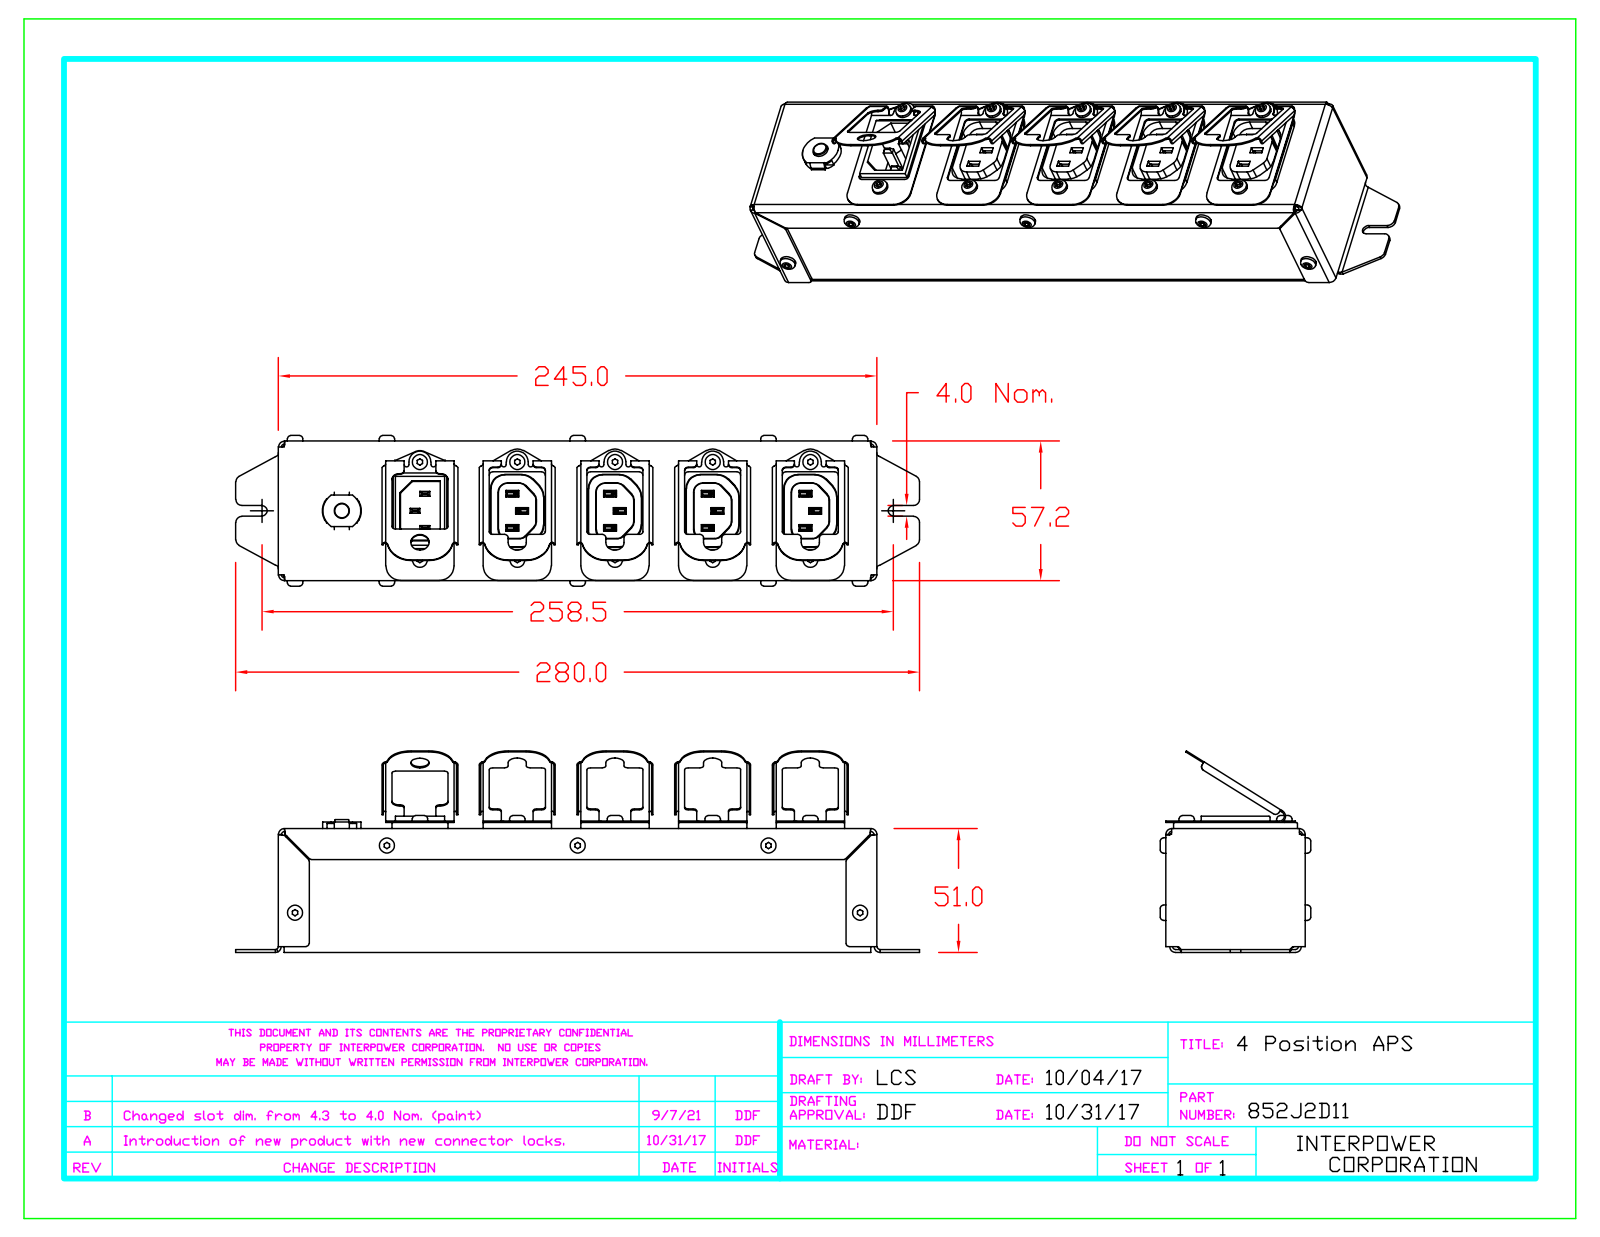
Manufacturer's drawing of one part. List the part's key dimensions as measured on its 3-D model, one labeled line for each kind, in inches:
Part name (STEP PRODUCT): 55001092_TOP-FAB; 55001092_GRDTAB; 55001092_ASM; 83030100_C14SURF_INET (+8 more)
STEP written by: PRO/ENGINEER BY PARAMETRIC TECHNOLOGY CORPORATION, 2011330 (CONFIG_CONTROL_DESIGN)
Units: inches
Bodies: 57 solids, 9055 faces (6916 planar, 1663 cylindrical, 476 other)
Overall size (bounding box): 11.024 × 3.251 × 2.43
Volume: 8.008 in³ · Surface area: 303.7 in²
Round holes (diameter × count): ⌀0.122 ×15, ⌀0.177 ×10, ⌀0.138 ×8, ⌀0.248 ×8, ⌀0.07 ×5, ⌀0.169 ×5, ⌀0.064 ×2, ⌀0.065 ×2, ⌀0.236 ×2, ⌀0.25 ×1, ⌀0.295 ×1
Round bosses / shafts (diameter × count): ⌀0.25 ×15, ⌀0.17 ×15, ⌀0.218 ×10, ⌀0.218 ×5, ⌀0.398 ×1, ⌀0.23 ×1
Partial cylindrical surfaces — rounded edges, fillets, slot ends (radius × count): R0.032 ×60, R0.059 ×60, R0.016 ×50, R0.025 ×50, R0.047 ×42, R0.02 ×38, R0.236 ×34, R0.039 ×29
Main face-to-face distances: 0.048, 2.077, 1.952, 2.029, 2.125, 2, 1.904, 1.575, 0.062, 2.139
Hole centre spacings: 1.575, 2.227, 3.15, 0.587, 1.101, 3.521, 1.385, 1.67
